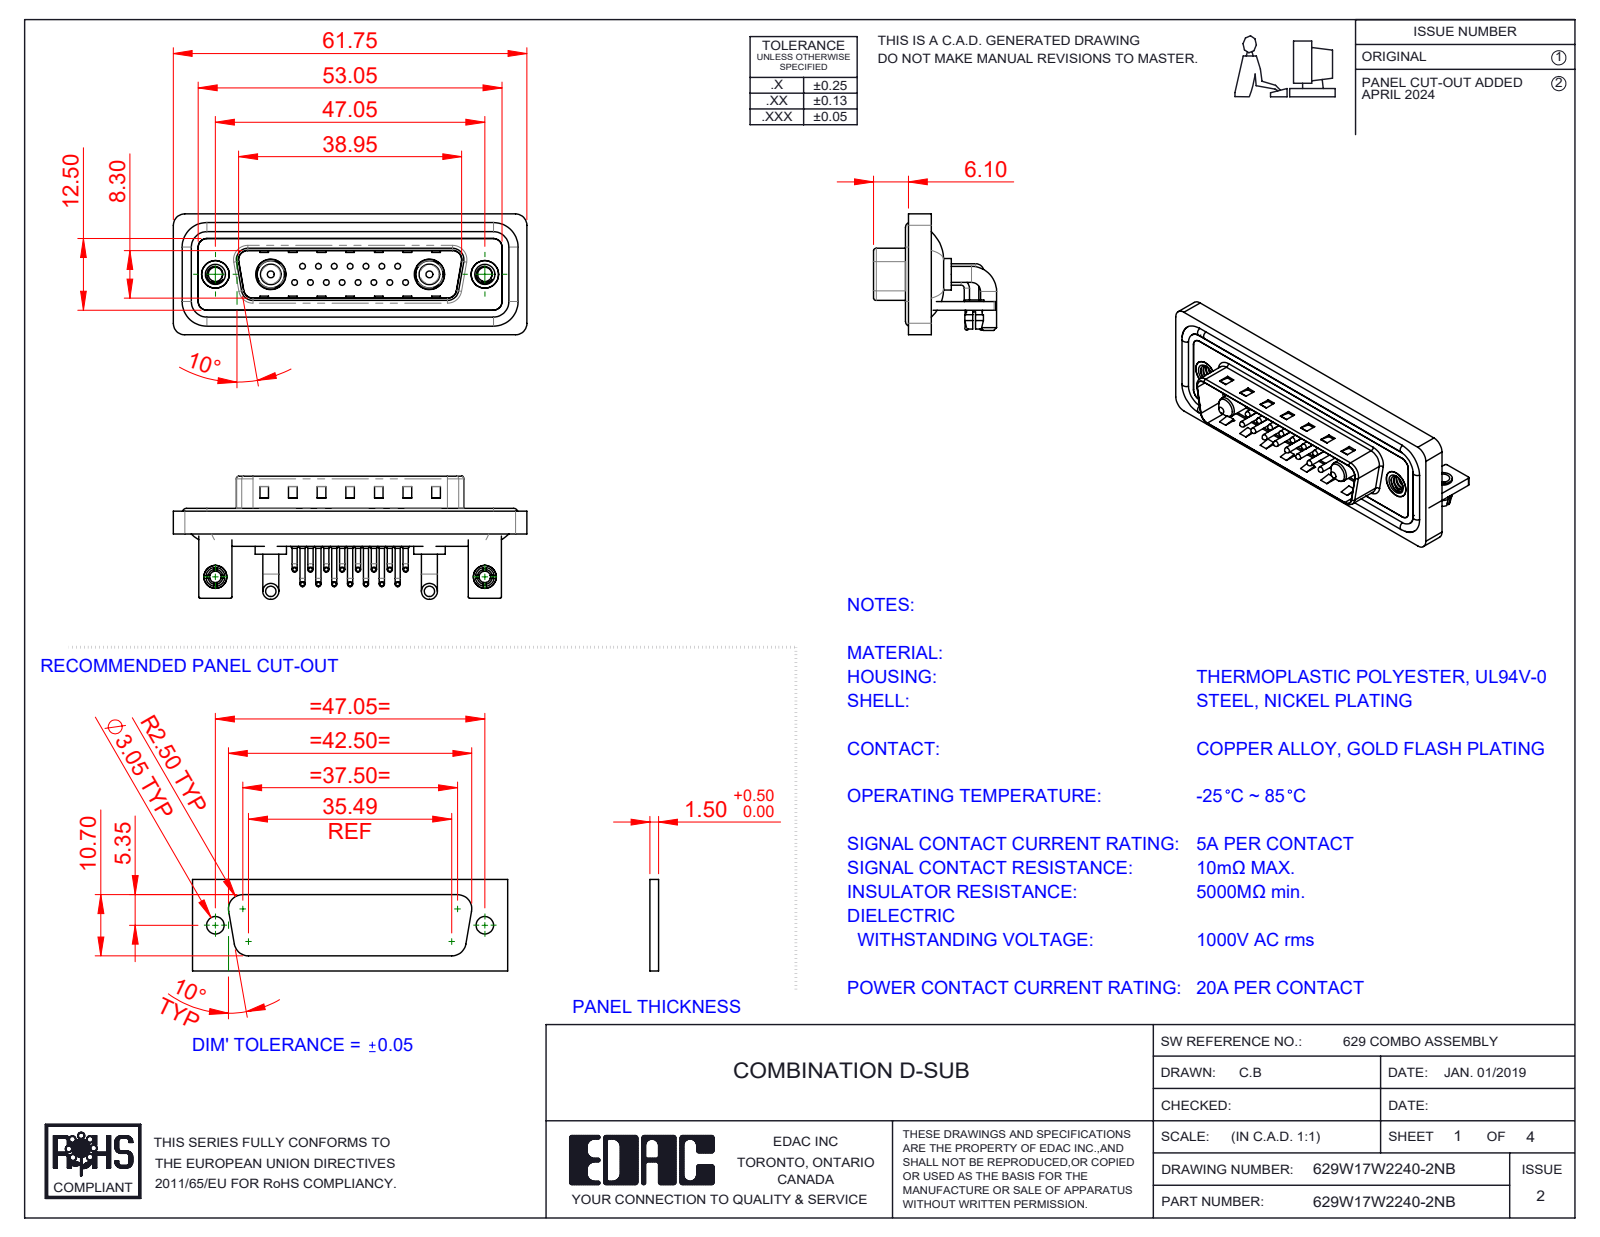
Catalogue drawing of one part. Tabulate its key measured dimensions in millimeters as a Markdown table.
| quantity | value |
| --- | --- |
| part name | 629Combo Housing_17W2; 629Combo Contact Row 1; 629Combo Contact Row 2; 629Combo Shell Front_25 Contacts (+7 more) |
| STEP written by | SolidWorks 2023 (CONFIG_CONTROL_DESIGN) |
| units | millimeters |
| bodies | 30 solids, 2349 faces (1257 planar, 820 cylindrical, 272 other) |
| overall size | 61.75 × 21.5 × 21.1 |
| volume | 7 820 mm³ |
| surface area | 13 399 mm² |
| round holes (diameter × count) | 2 × 17, 0.75 × 15, 1.6 × 15, 2.5 × 4, 3.2 × 2, 4 × 2, 4.8 × 2, 4.85 × 2, 5 × 2, 5.3 × 2 |
| round bosses / shafts (diameter × count) | 0.9 × 30, 1.5 × 15, 1 × 15, 0.65 × 15, 2.8 × 4, 1.6 × 4, 5.5 × 2, 5.2 × 2 |
| partial cylindrical surfaces (radius × count) | 2 × 19, 1.5 × 18, 0.25 × 16, 1.01 × 15, 0.5 × 9, 1.6 × 8, 0.6 × 4, 0.65 × 4 |
| main face-to-face distances | 0.4, 0.8, 1.5, 2.1, 2.9, 1.1, 4.1, 1.6, 4.5, 3.7 |
| hole center spacings | 3.16, 2.77, 5.54, 8.31, 5.04, 7.49, 11.08, 5.03 |
